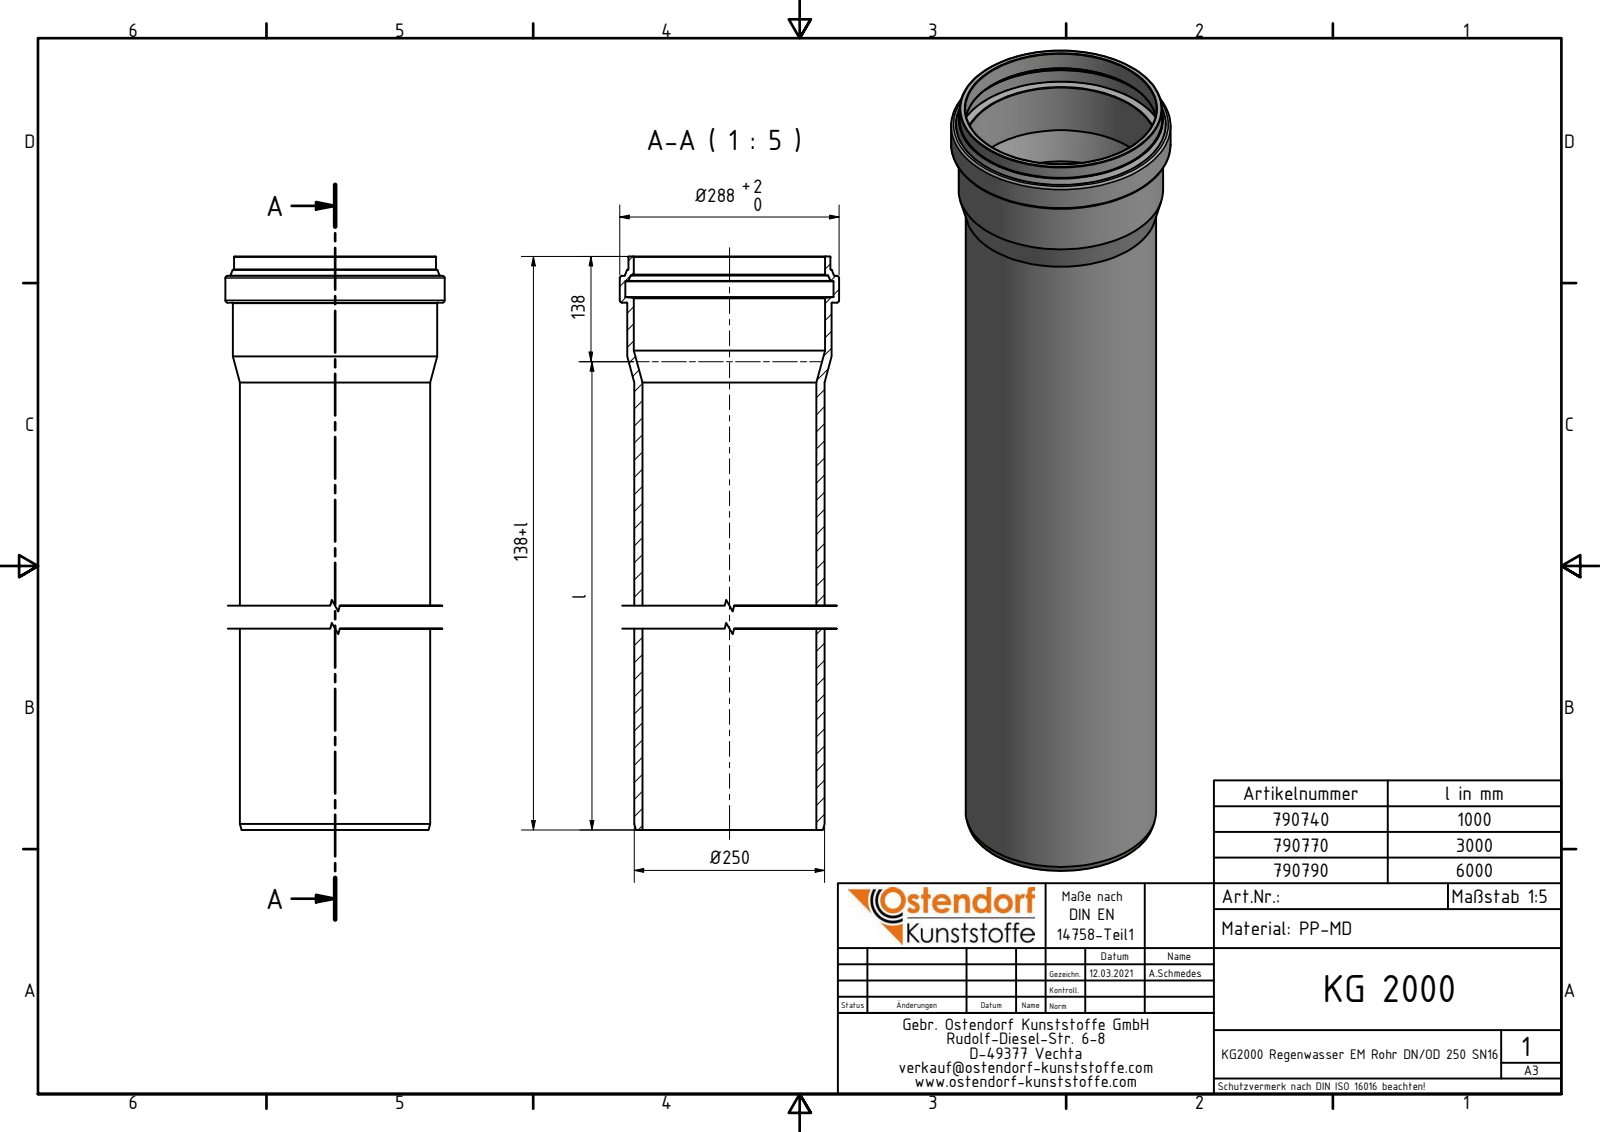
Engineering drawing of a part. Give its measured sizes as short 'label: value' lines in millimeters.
name: 790790 KG2000EM Rohr-Passlängen Regenwasser DN250x6000 SN16
written by: Autodesk Inventor 2020 (AUTOMOTIVE_DESIGN)
unit: mm
bodies: 1 solid, 35 faces (5 planar, 8 cylindrical, 22 other)
size: 6138 × 288 × 288
volume: 49 740 000 mm³; area: 9 289 000 mm²
holes: 1× ⌀228.4, 1× ⌀251, 1× ⌀273.6
bosses: 1× ⌀288, 1× ⌀268.4, 1× ⌀265.4, 1× ⌀250
face distances: 6077.4, 6138, 60.6, 6112.7, 35.3, 25.3, 6120.59, 43.19, 7.89, 17.41
